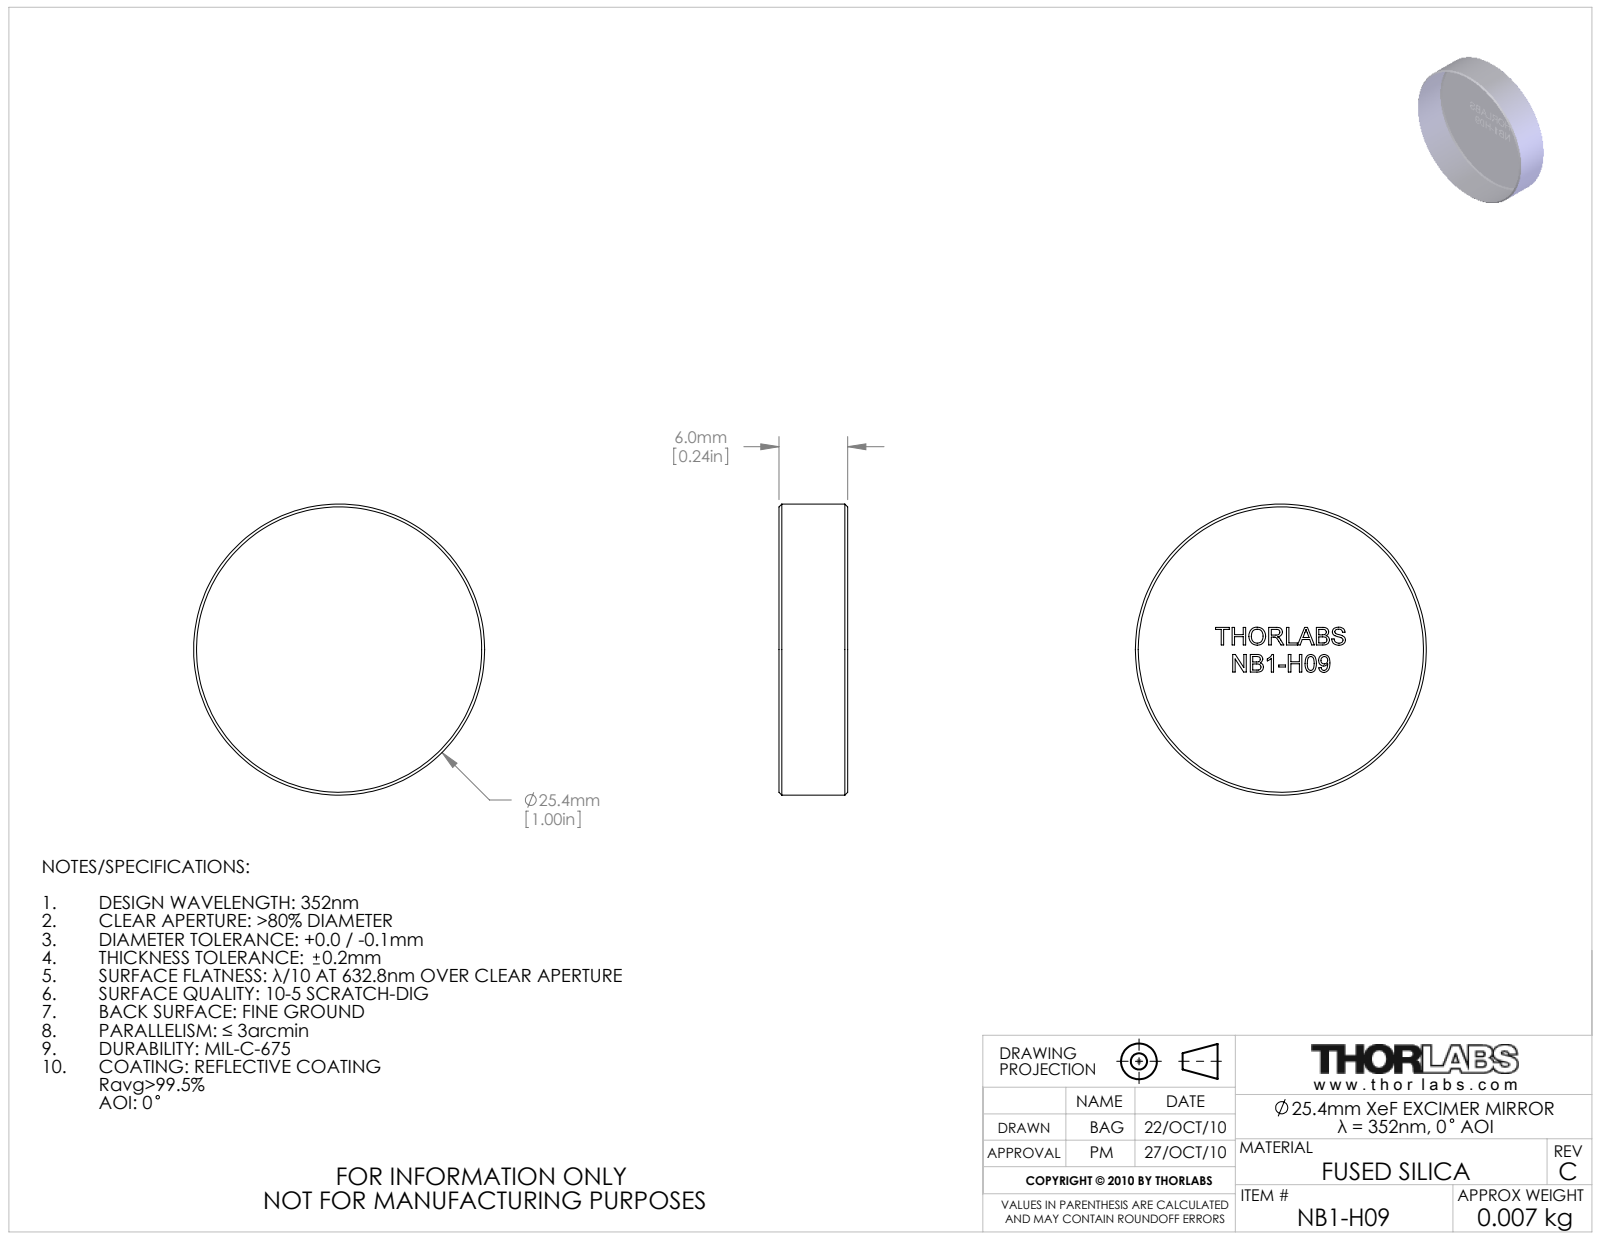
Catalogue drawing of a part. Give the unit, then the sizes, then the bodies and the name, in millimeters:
Units: millimetres
Overall size (bounding box): 25.4 × 25.4 × 6
Round bosses / shafts (diameter × count): ⌀25.4 ×1
Main face-to-face distances: 6, 1.5, 4.9, 2.4, 2.2, 1, 1.4, 2.4, 1.2, 3.7
Volume: 3 030 mm³ · Surface area: 1 468 mm²
Bodies: 1 solid, 209 faces (126 planar, 2 cylindrical, 81 other)
Part name (STEP PRODUCT): 5382-E0W
STEP written by: SolidWorks 2009 (AUTOMOTIVE_DESIGN)
